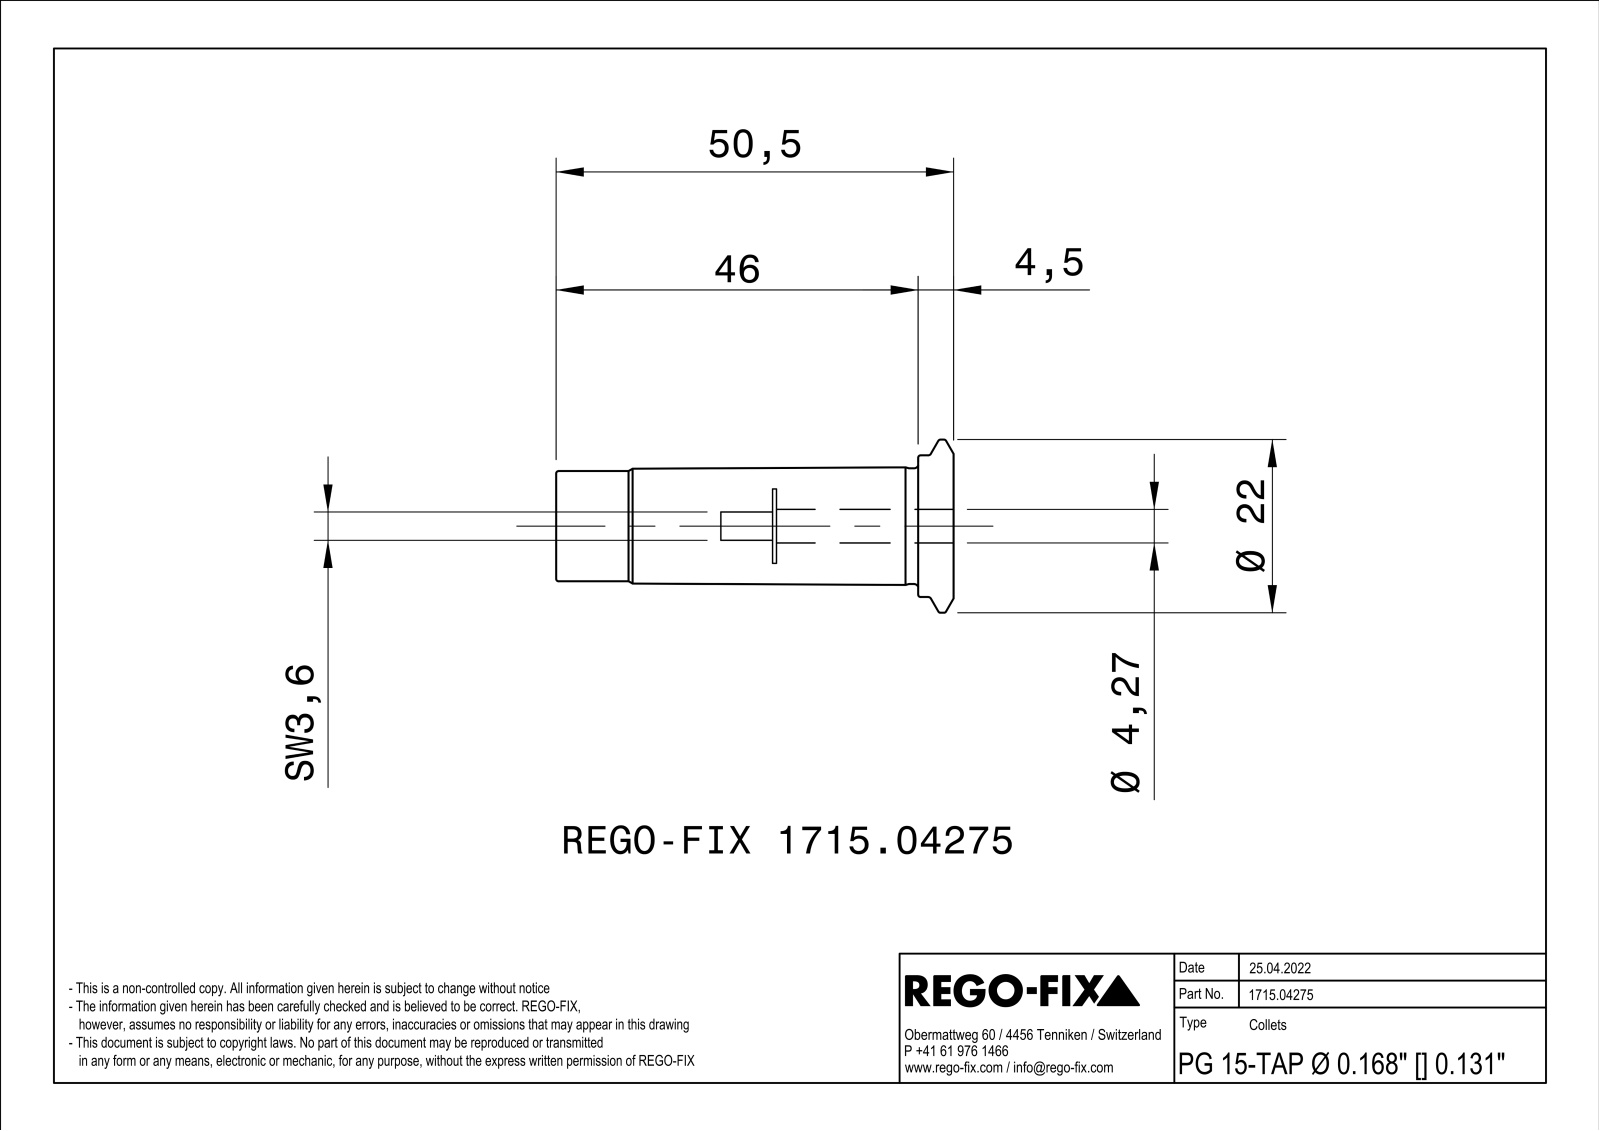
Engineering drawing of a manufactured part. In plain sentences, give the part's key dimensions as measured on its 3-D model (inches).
The part is named "NOCUT". Its 3-D file was written by "SIEMENS PLM Software Solid Edge ST10 (AUTOMOTIVE_DESIGN)". It is 1 solid with 101 faces: 25 planar, 28 cylindrical and 48 other. Overall it measures 1.988 by 0.866 by 0.866 inches. Its volume is 0.431 cubic inches and its surface area 9.432 square inches. Round holes: 1 of diameter 0.272, 1 of diameter 0.276, 1 of diameter 0.331, 1 of diameter 0.437. Round bosses or shafts: 1 of diameter 0.866, 1 of diameter 0.709, 1 of diameter 0.579, 1 of diameter 0.551, 1 of diameter 0.433, 1 of diameter 0.429, 1 of diameter 0.413, 1 of diameter 0.402. Partial cylindrical surfaces (rounded edges, fillets, slot ends): 1 of radius 0.084. The main face-to-face distances are 0.039, 1.988, 0.142, 0.886, 1.102, 0.906, 0.02, 1.083, 0.177, 0.276.
